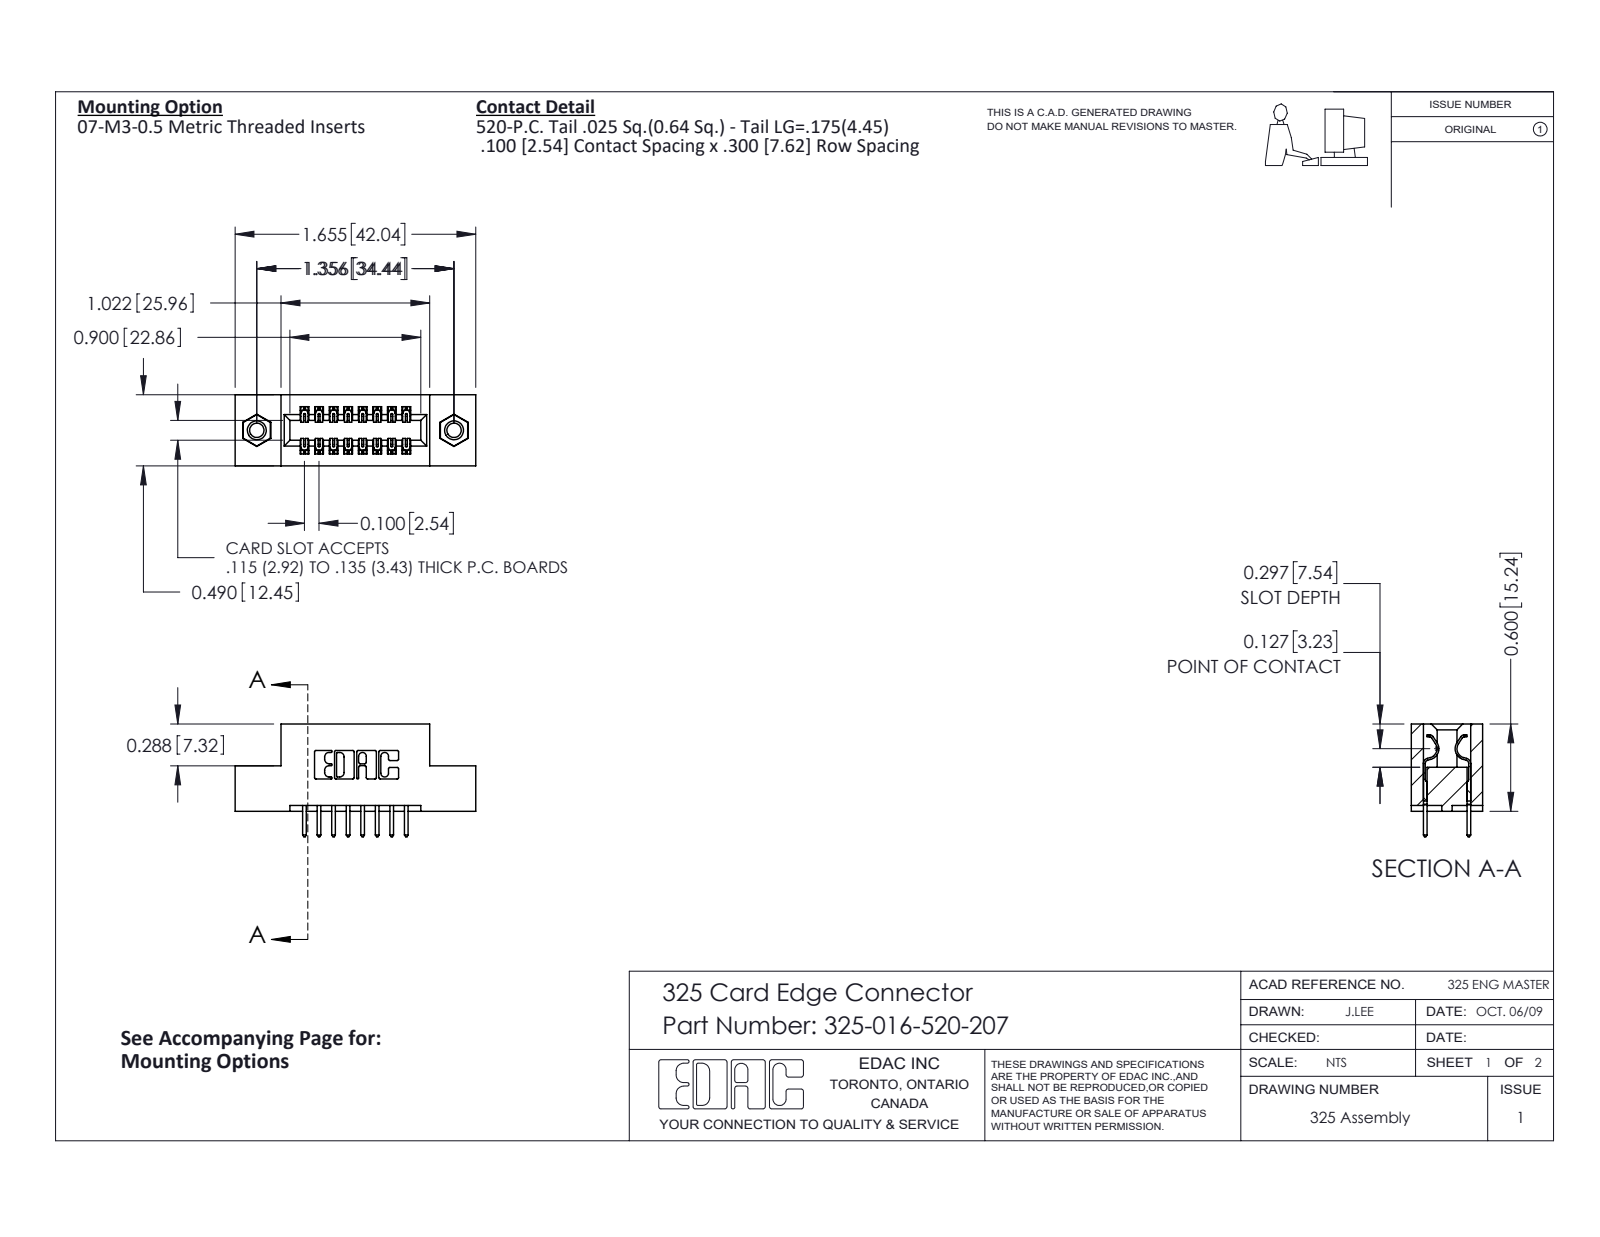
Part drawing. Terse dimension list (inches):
name: 325 Part_TI; 345-250-001_345-250-005-103; 325-016-520-207; 325-292-001_325-293-120
written by: SolidWorks 2016 (CONFIG_CONTROL_DESIGN)
unit: in
bodies: 19 solids, 1006 faces (678 planar, 312 cylindrical, 16 other)
size: 1.655 × 0.775 × 0.49
volume: 0.312 in³; area: 8.32 in²
holes: 2× ⌀0.098, 2× ⌀0.125, 2× ⌀0.16
bosses: 2× ⌀0.155
rounds: 24× R0.006, 22× R0.01, 16× R0.01, 6× R0.007, 6× R0.031, 3× R0.026, 2× R0.014, 2× R0.022
face distances: 0.3, 0.1, 0.2, 0.083, 0.407, 0.04, 0.49, 0.06, 0.4, 0.6
hole spacings: 1.356
